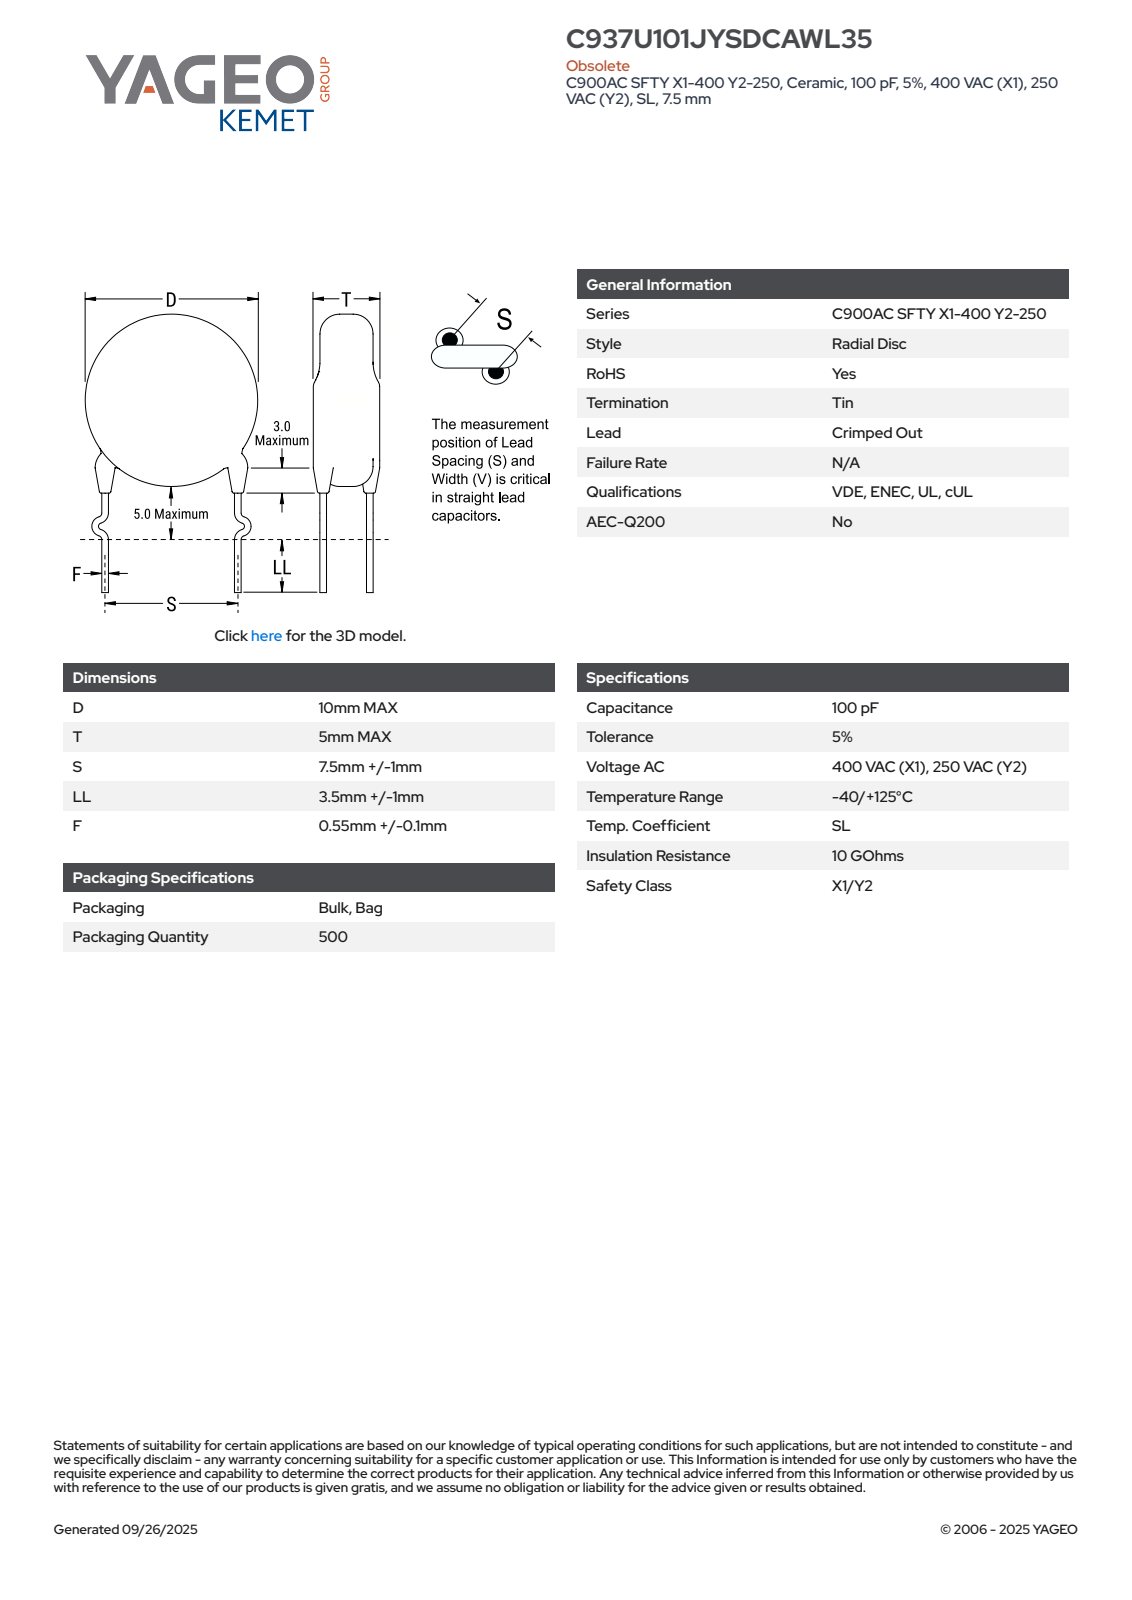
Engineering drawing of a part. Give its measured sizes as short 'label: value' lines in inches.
name: CCD_KCOC900_D10T5S7.5LL4.5F0.55
written by: SolidWorks 2014 (AUTOMOTIVE_DESIGN)
unit: in
bodies: 4 solids, 85 faces (63 planar, 6 cylindrical, 16 other)
size: 0.768 × 0.49 × 0.197
volume: 0.024 in³; area: 0.546 in²
bosses: 2× ⌀0.047, 1× ⌀0.394
face distances: 0.197, 0.041, 0.218, 0.177, 0.033, 0.167, 0.015, 0.178, 0.121, 0.126
